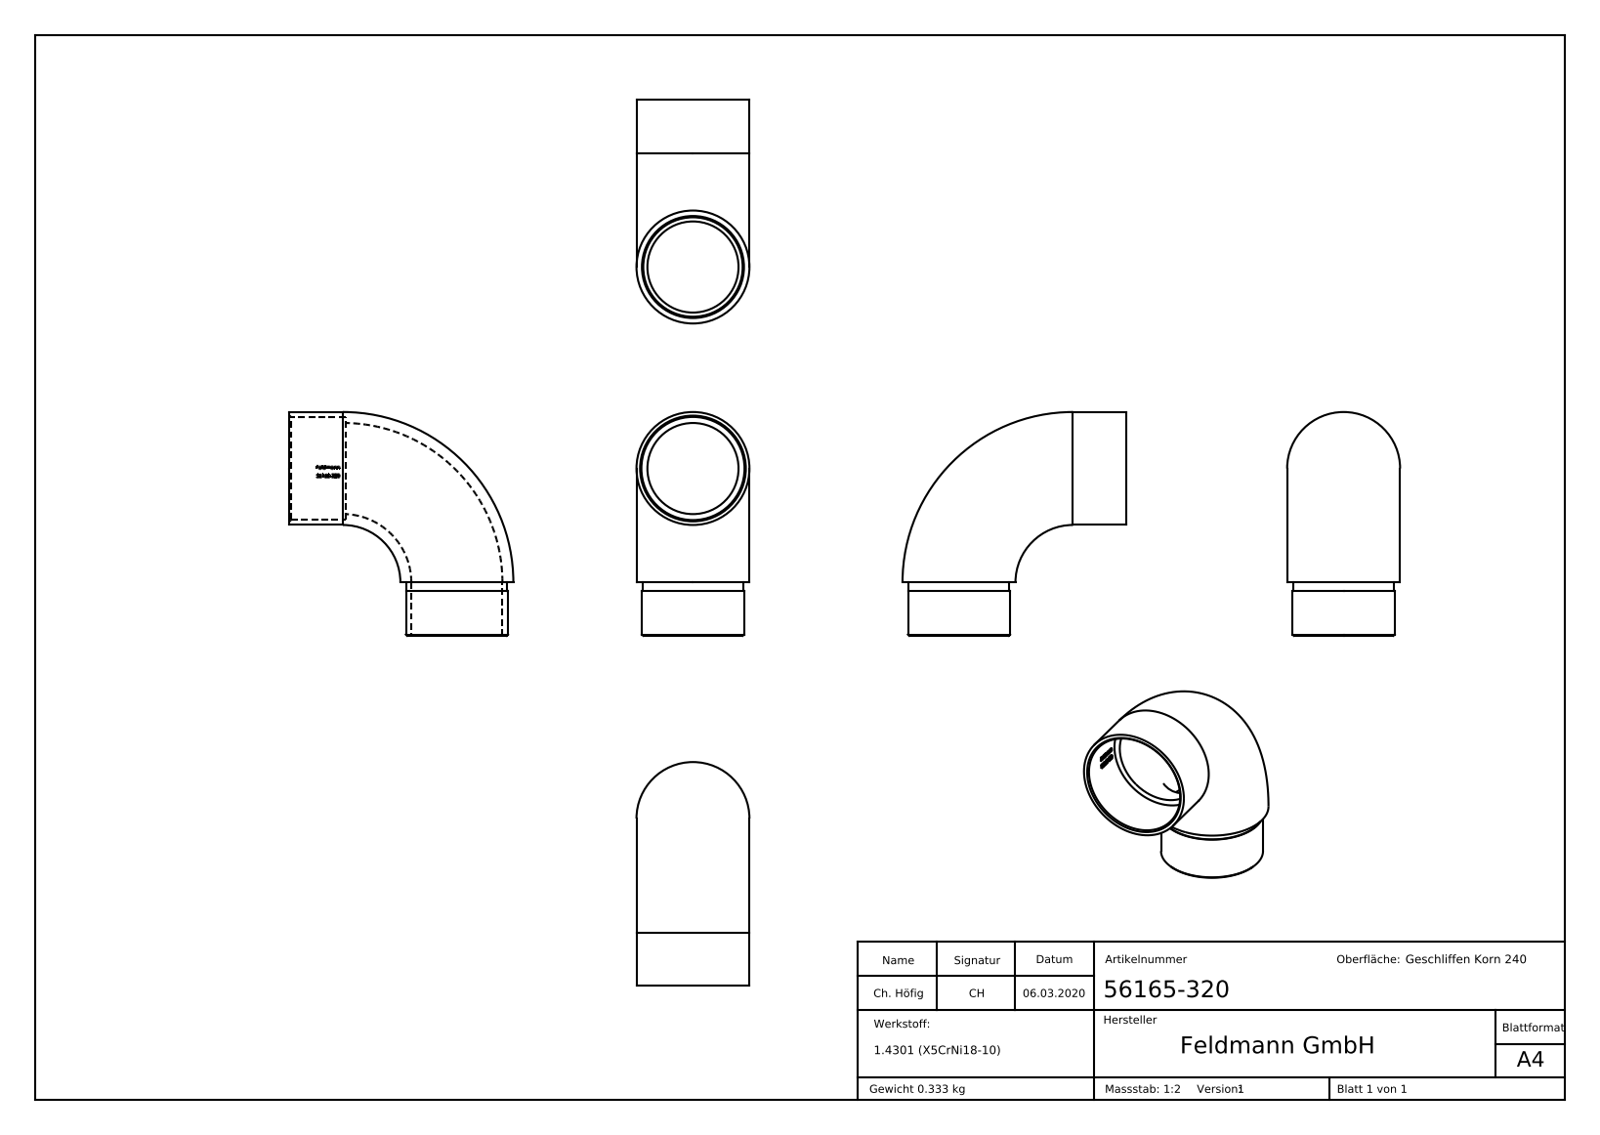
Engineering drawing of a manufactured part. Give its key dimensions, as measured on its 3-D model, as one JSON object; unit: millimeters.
{"part_name": "56165-320", "step_written_by": "SolidWorks 2015 (CONFIG_CONTROL_DESIGN)", "units": "millimeters", "bodies": {"solids": 1, "faces": 239, "planar": 113, "cylindrical": 11, "other": 115}, "overall_size": [84, 84, 42.4], "volume_mm3": 42184, "surface_area_mm2": 26875, "round_holes": [[34.2, 1], [38.7, 1]], "round_bosses_or_shafts": [[42.4, 1], [38.3, 1], [37.9, 1]], "face_to_face_distances": [21, 20, 17, 3, 2.02, 1.32, 0.39, 0.88, 0.38, 4.08]}
